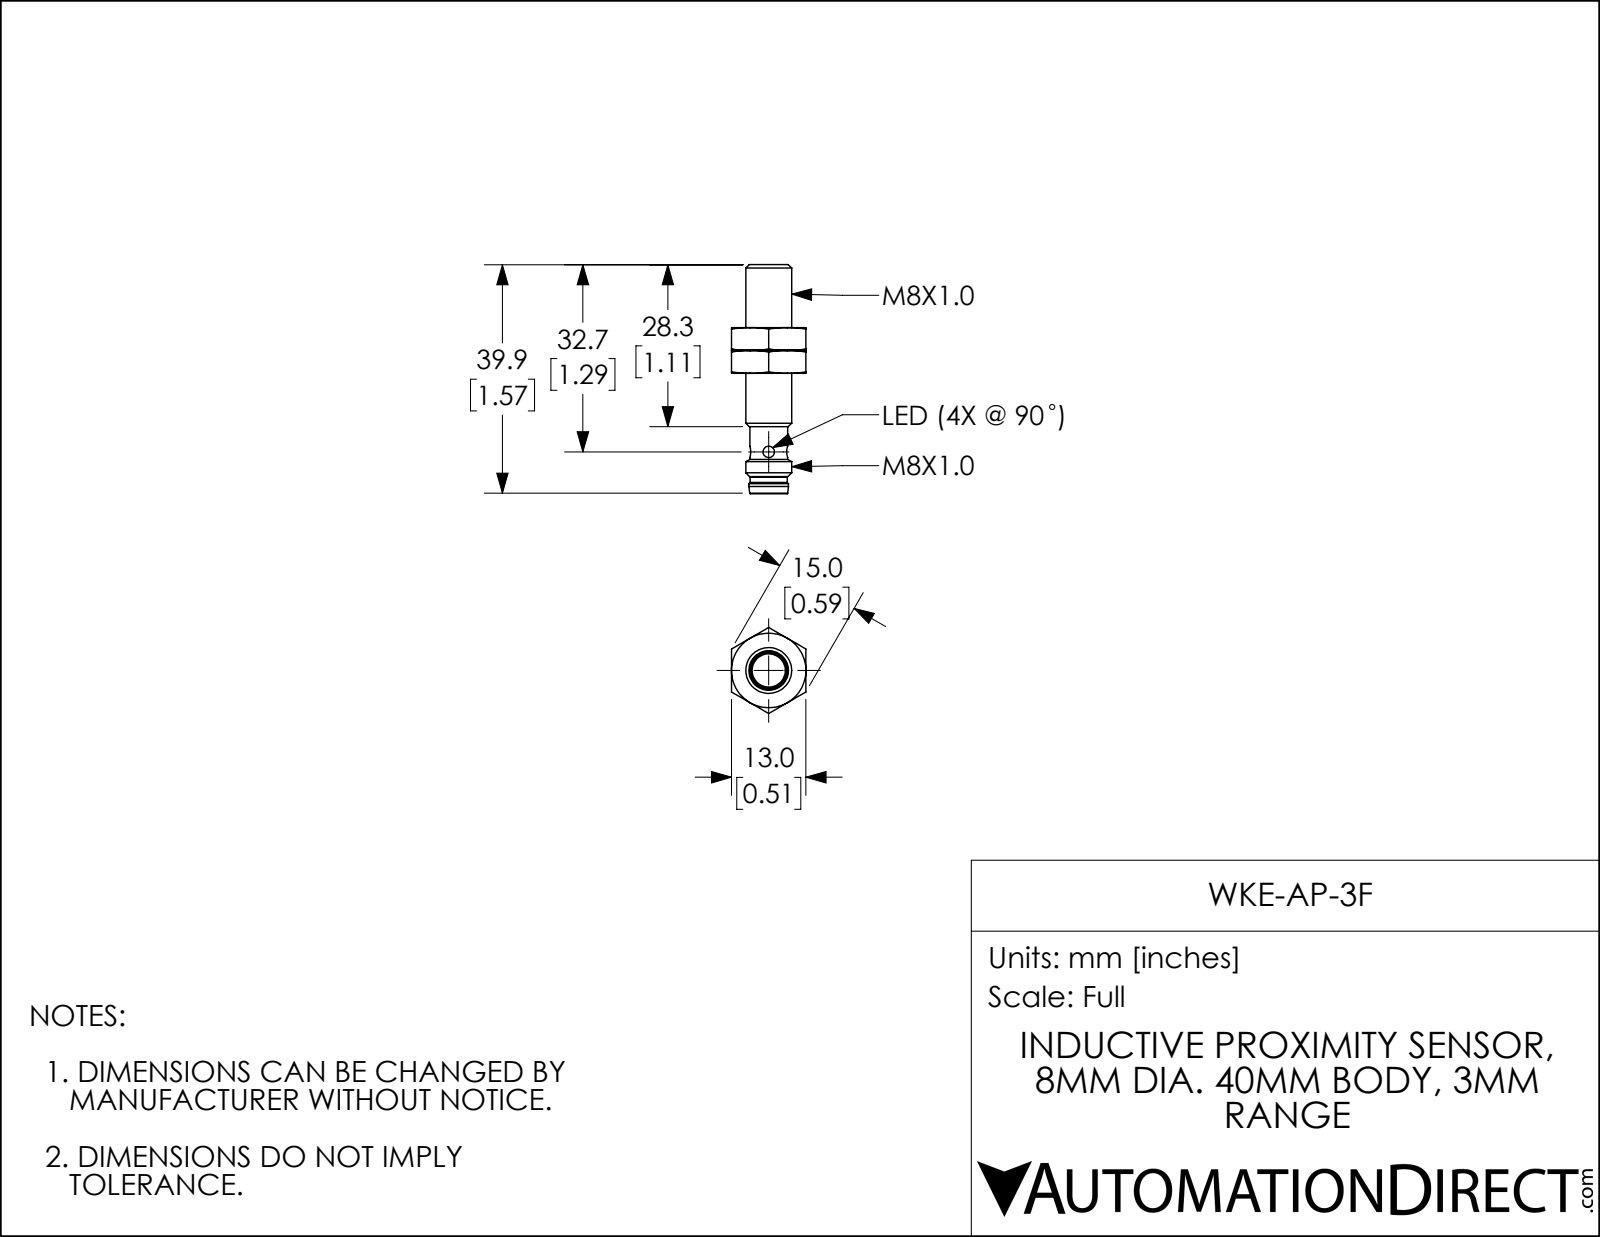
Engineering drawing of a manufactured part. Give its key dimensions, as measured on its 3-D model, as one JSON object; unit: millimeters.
{"part_name": "WKE-AP-3F", "step_written_by": "SolidWorks 2017 (AUTOMOTIVE_DESIGN)", "units": "millimeters", "bodies": {"solids": 3, "faces": 77, "planar": 22, "cylindrical": 18, "other": 37}, "overall_size": [40, 15, 13], "volume_mm3": 2570, "surface_area_mm2": 2096, "round_holes": [[2, 2], [5.8, 1], [6.5, 1], [6.9, 1]], "round_bosses_or_shafts": [[8, 1], [6.9, 1], [6.6, 1], [6.5, 1], [6.4, 1]], "partial_cylinders_radius": [[2.9, 1]], "face_to_face_distances": [13, 4, 8, 18.9, 15, 10.9, 16, 19.9, 24, 34.9]}
